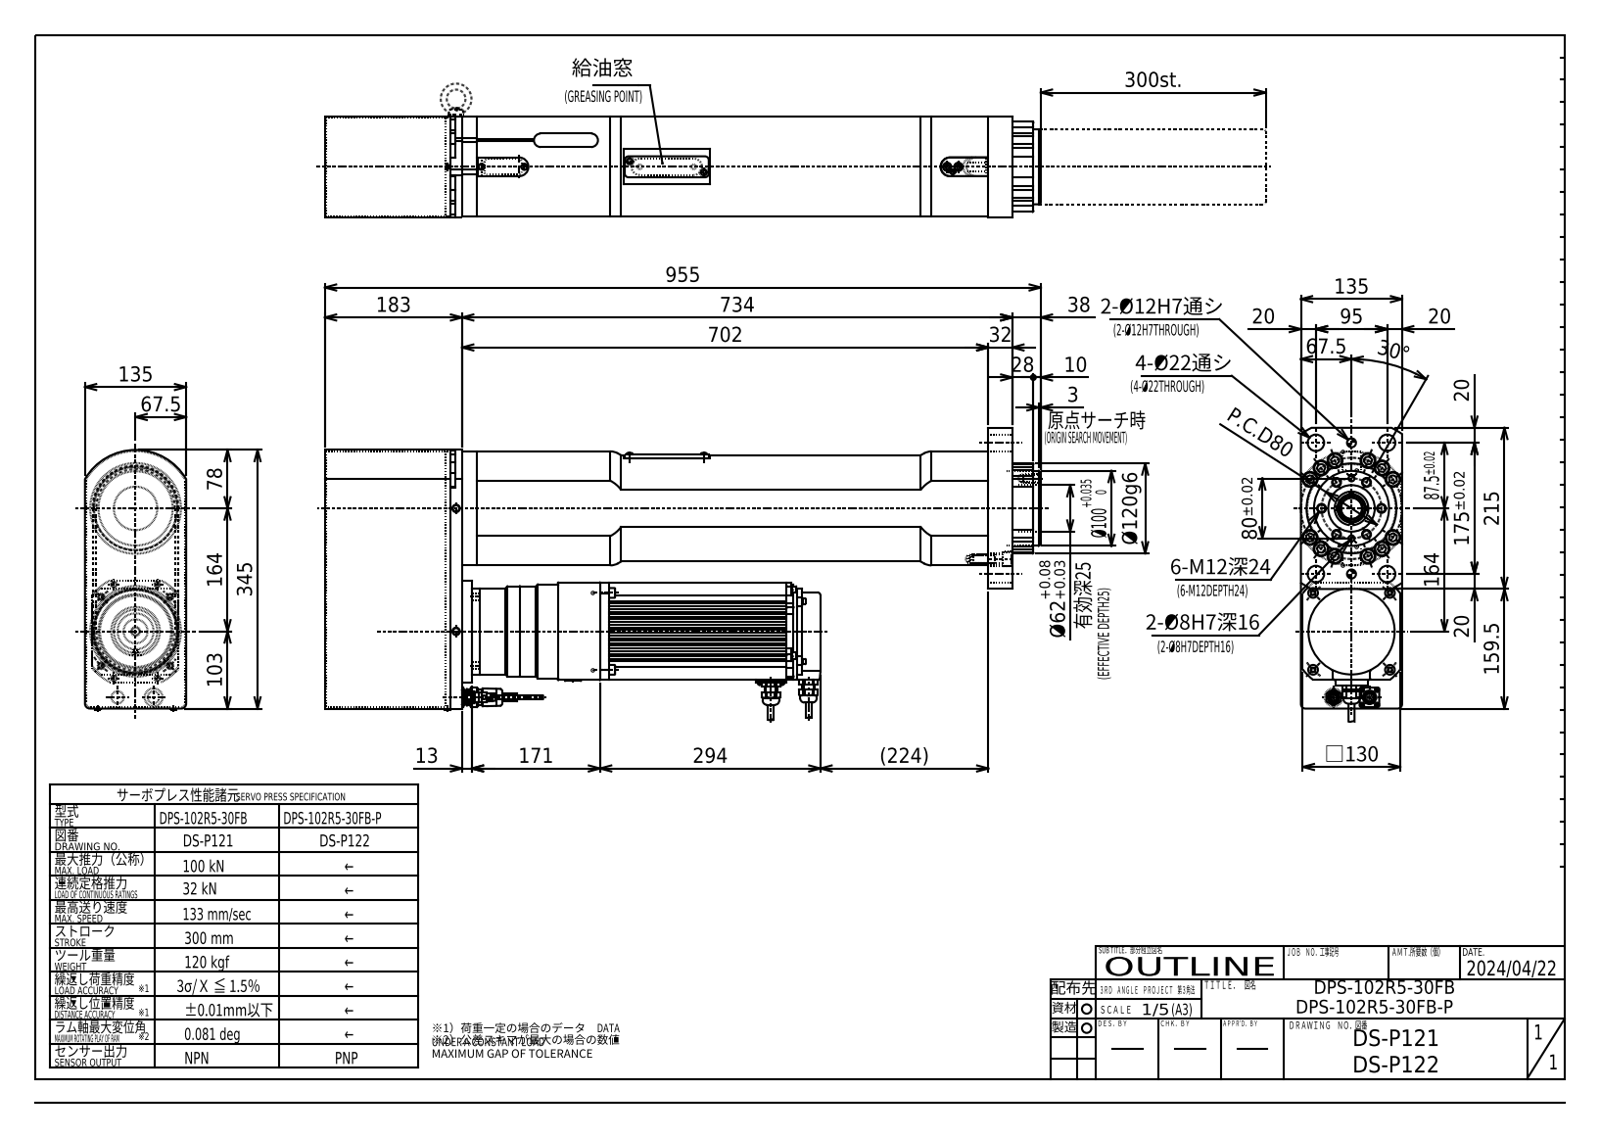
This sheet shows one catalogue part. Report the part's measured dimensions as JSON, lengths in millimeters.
{"part_name": "DPS-102R5-30FB(-P)(DS-P121_P122)_OUTLINE; DPS-102R5-30FB(DS-P121)_BODY; DPS-102(300st)_SHAFT", "step_written_by": "Autodesk Inventor 2023 (CONFIG_CONTROL_DESIGN)", "units": "millimeters", "bodies": {"solids": 2, "faces": 1687, "planar": 909, "cylindrical": 406, "other": 372}, "overall_size": [956.5, 388.51, 135], "volume_mm3": 25910000, "surface_area_mm2": 1398000, "round_holes": [[6.65, 12], [1, 8], [1.1, 7], [10.11, 6], [11, 5], [1.2, 4], [3.24, 4], [4.5, 4], [4.92, 4], [8, 4], [9, 4], [9.1, 4]], "round_bosses_or_shafts": [[18, 9], [1.6, 8], [4, 7], [1.55, 7], [1, 7], [8, 5], [8.5, 4], [6, 4]], "partial_cylinders_radius": [[5, 43], [2, 19], [1, 9], [2.5, 9], [3, 9], [10, 6], [4, 5], [4.25, 4]], "face_to_face_distances": [1, 3, 134, 6, 135, 9, 68, 133, 71, 65], "hole_center_spacings": [3, 97.37, 5.2, 7.51, 10.26, 23.69, 24.94, 47.5]}
